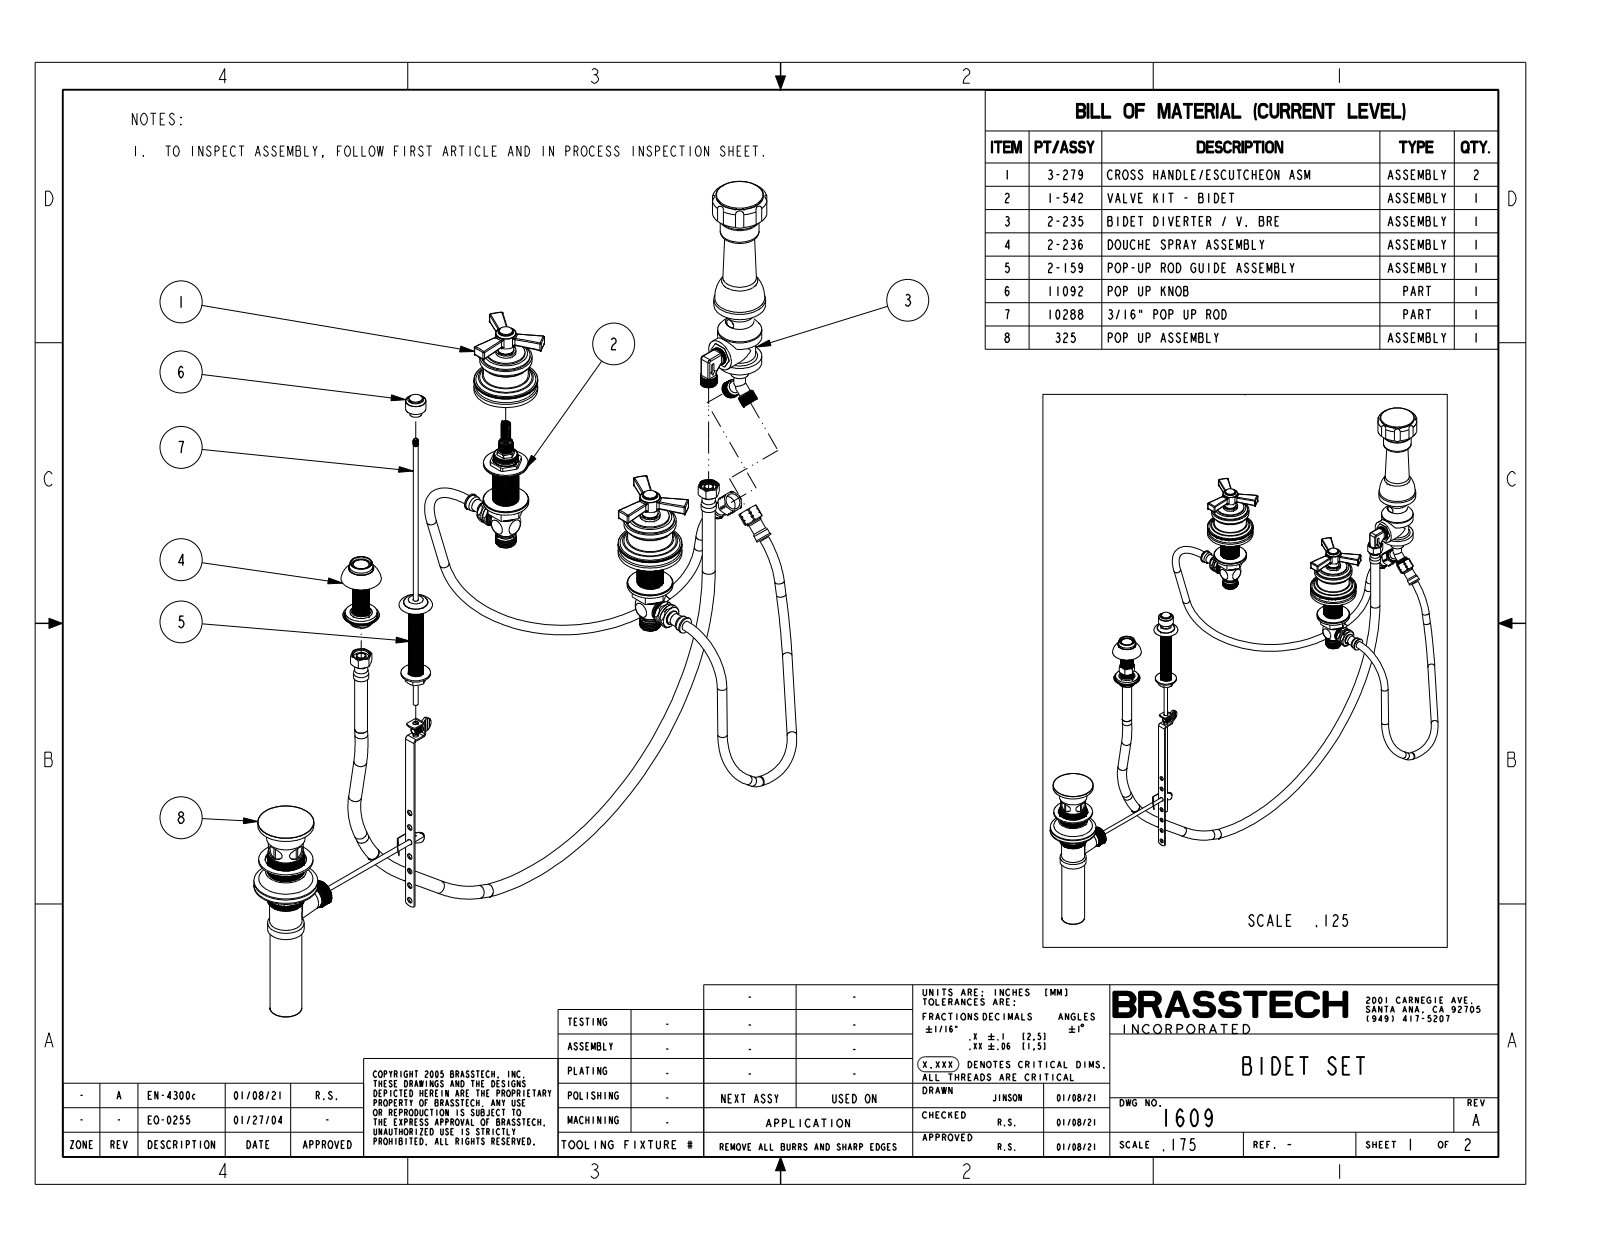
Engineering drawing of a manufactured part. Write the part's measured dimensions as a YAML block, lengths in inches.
part_name: "1609"
step_written_by: "CREO PARAMETRIC BY PTC INC, 2018400 (CONFIG_CONTROL_DESIGN)"
units: inches
bodies: {solids: 5, faces: 1511, planar: 809, cylindrical: 476, other: 226}
overall_size: [22.856, 10.84, 5.353]
volume: 25.75
surface_area: 110.2
round_holes:
  - {diameter: 0.625, count: 1}
  - {diameter: 0.792, count: 1}
  - {diameter: 0.94, count: 1}
round_bosses_or_shafts:
  - {diameter: 0.8, count: 3}
  - {diameter: 0.525, count: 3}
  - {diameter: 2.5, count: 2}
  - {diameter: 2.4, count: 2}
  - {diameter: 2.05, count: 2}
  - {diameter: 1.9, count: 2}
  - {diameter: 1.75, count: 2}
  - {diameter: 1.5, count: 2}
partial_cylinders:
  - {radius: 0.04, count: 12}
  - {radius: 0.1, count: 12}
  - {radius: 0.21, count: 8}
  - {radius: 0.357, count: 1}
  - {radius: 1.077, count: 1}
face_to_face_distances: [1.775, 0.2, 0.1, 1.375, 1.3, 0.15, 0.4, 0.9, 1.1, 1.25]
